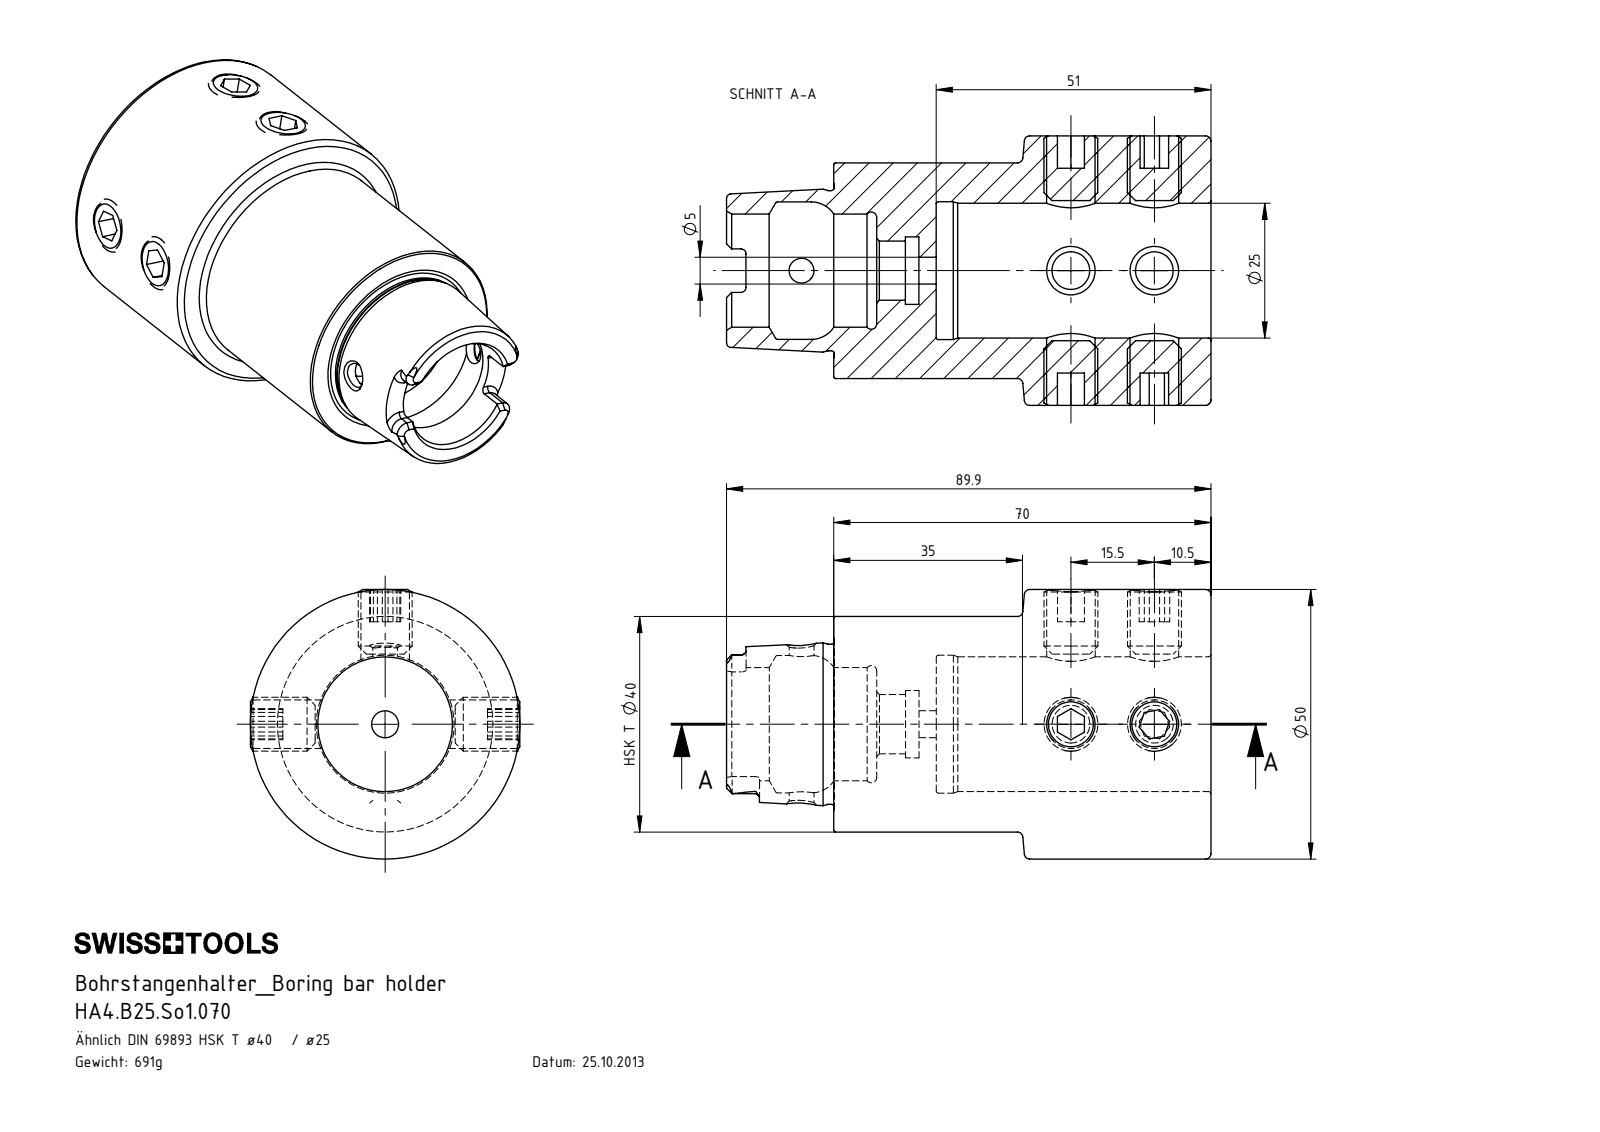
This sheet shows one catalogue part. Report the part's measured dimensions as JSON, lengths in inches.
{"part_name": "ISO 4026 - M10 x 12_PreviewCfg; HA4.B25.So1.070; HA4-B25.So1.070_A_Fertigbearbeitung", "step_written_by": "SolidWorks 2017 (CONFIG_CONTROL_DESIGN)", "units": "inches", "bodies": {"solids": 7, "faces": 232, "planar": 78, "cylindrical": 62, "other": 92}, "overall_size": [3.539, 1.969, 1.969], "volume_in3": 5.371, "surface_area_in2": 41.16, "round_holes": [[0.354, 4], [0.181, 1], [0.197, 1], [0.433, 1], [0.492, 1], [0.827, 1], [0.984, 1], [1.004, 1], [1.008, 1]], "round_bosses_or_shafts": [[0.394, 4], [1.969, 1], [1.575, 1], [1.17, 1]], "partial_cylinders_radius": [[0.035, 6], [0.074, 4]], "face_to_face_distances": [2.008, 0.748, 2.756, 0.197, 0.236, 0.313, 0.435, 2.443, 0.783, 1.096], "hole_center_spacings": [0.61, 1.969, 2.579]}
